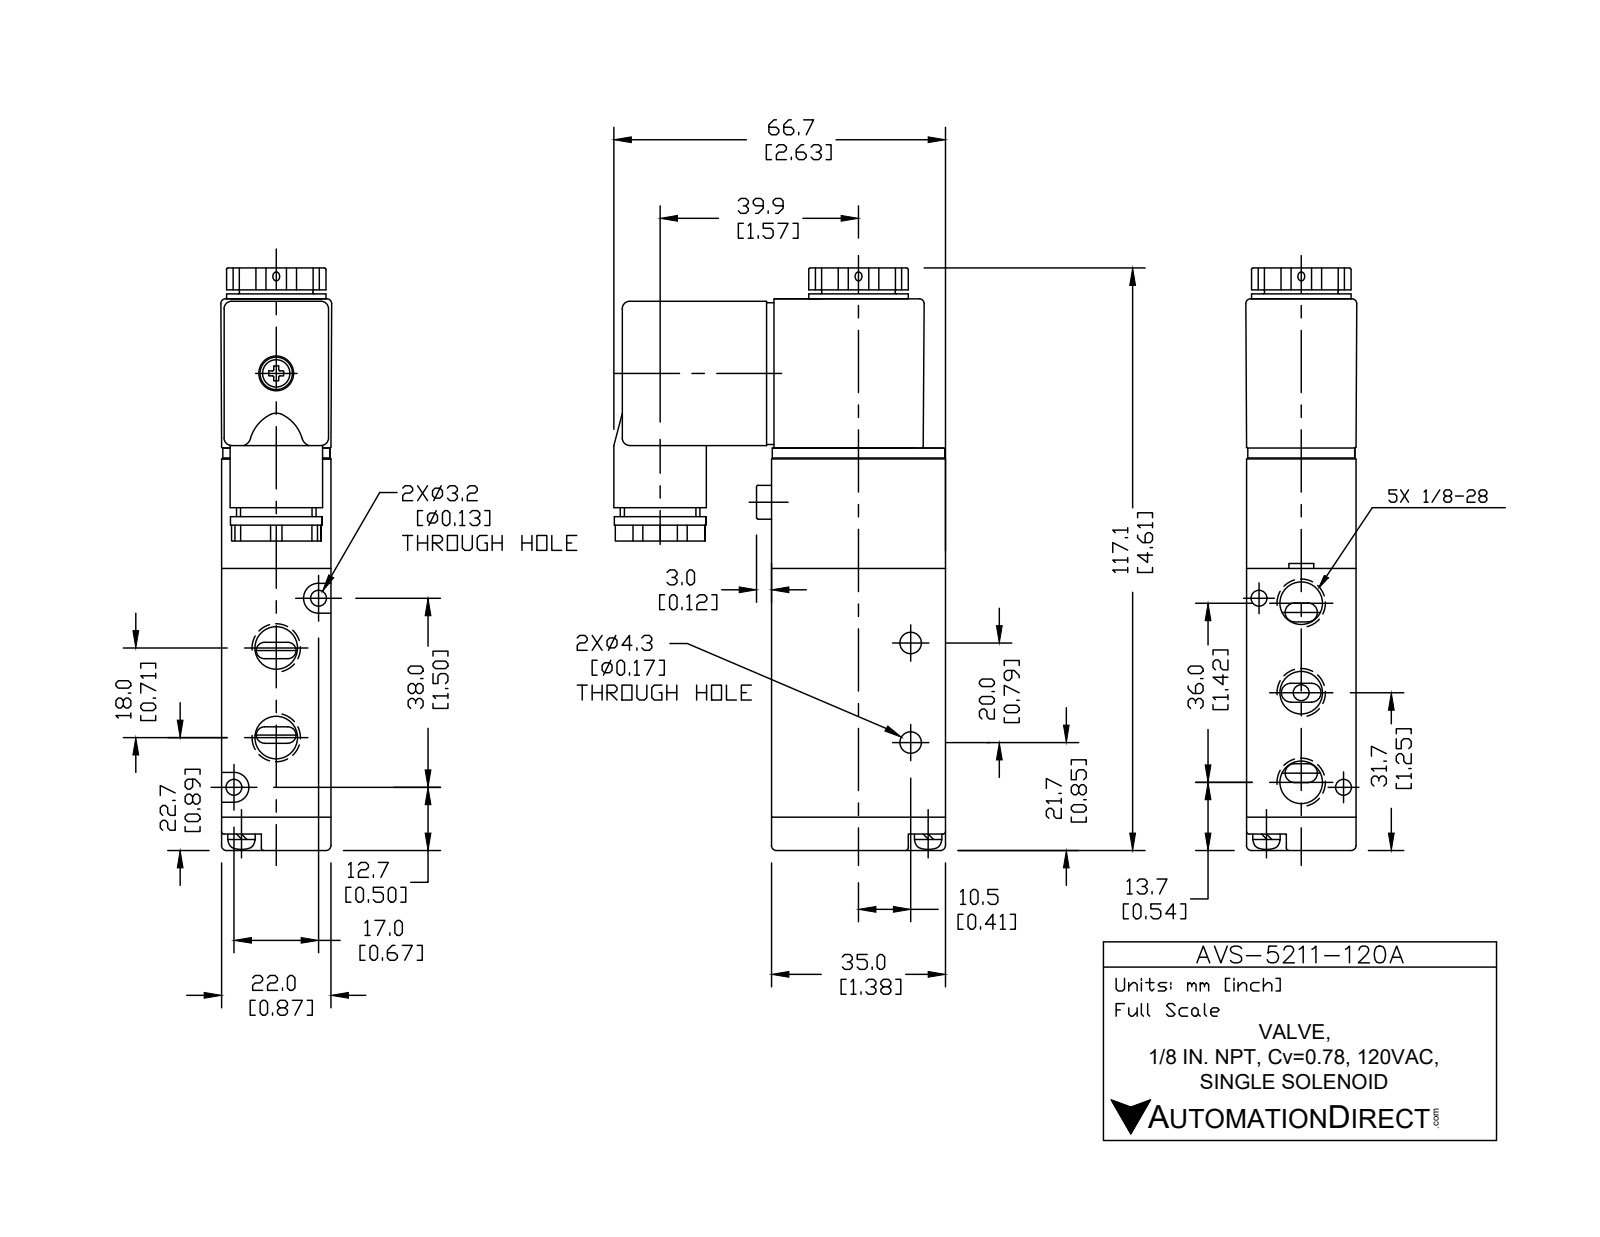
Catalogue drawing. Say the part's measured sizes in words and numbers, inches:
The part is named "AVS-5211-120A". Its 3-D file was written by "SolidWorks 2015 (CONFIG_CONTROL_DESIGN)". It is 4 solids with 195 faces: 91 planar, 77 cylindrical and 27 other. Overall it measures 4.61 by 2.626 by 0.866 inches. Its volume is 6.187 cubic inches and its surface area 38.27 square inches. Round holes: 5 of diameter 0.332, 2 of diameter 0.169, 1 of diameter 0.126, 1 of diameter 0.13, 1 of diameter 0.366. Round bosses or shafts: 1 of diameter 0.787, 1 of diameter 0.732, 1 of diameter 0.724, 1 of diameter 0.63, 1 of diameter 0.583, 1 of diameter 0.264. Partial cylindrical surfaces (rounded edges, fillets, slot ends): 12 of radius 0.059, 10 of radius 0.061, 8 of radius 0.02, 5 of radius 0.039, 2 of radius 0.118. The main face-to-face distances are 0.866, 0.02, 1.969, 0.846, 1.378, 0.264, 0.827, 4.346, 2.232, 1.181. The hole center spacings are 0.354, 0.709, 0.337, 0.517, 0.819, 1.063, 1.152, 1.494.
